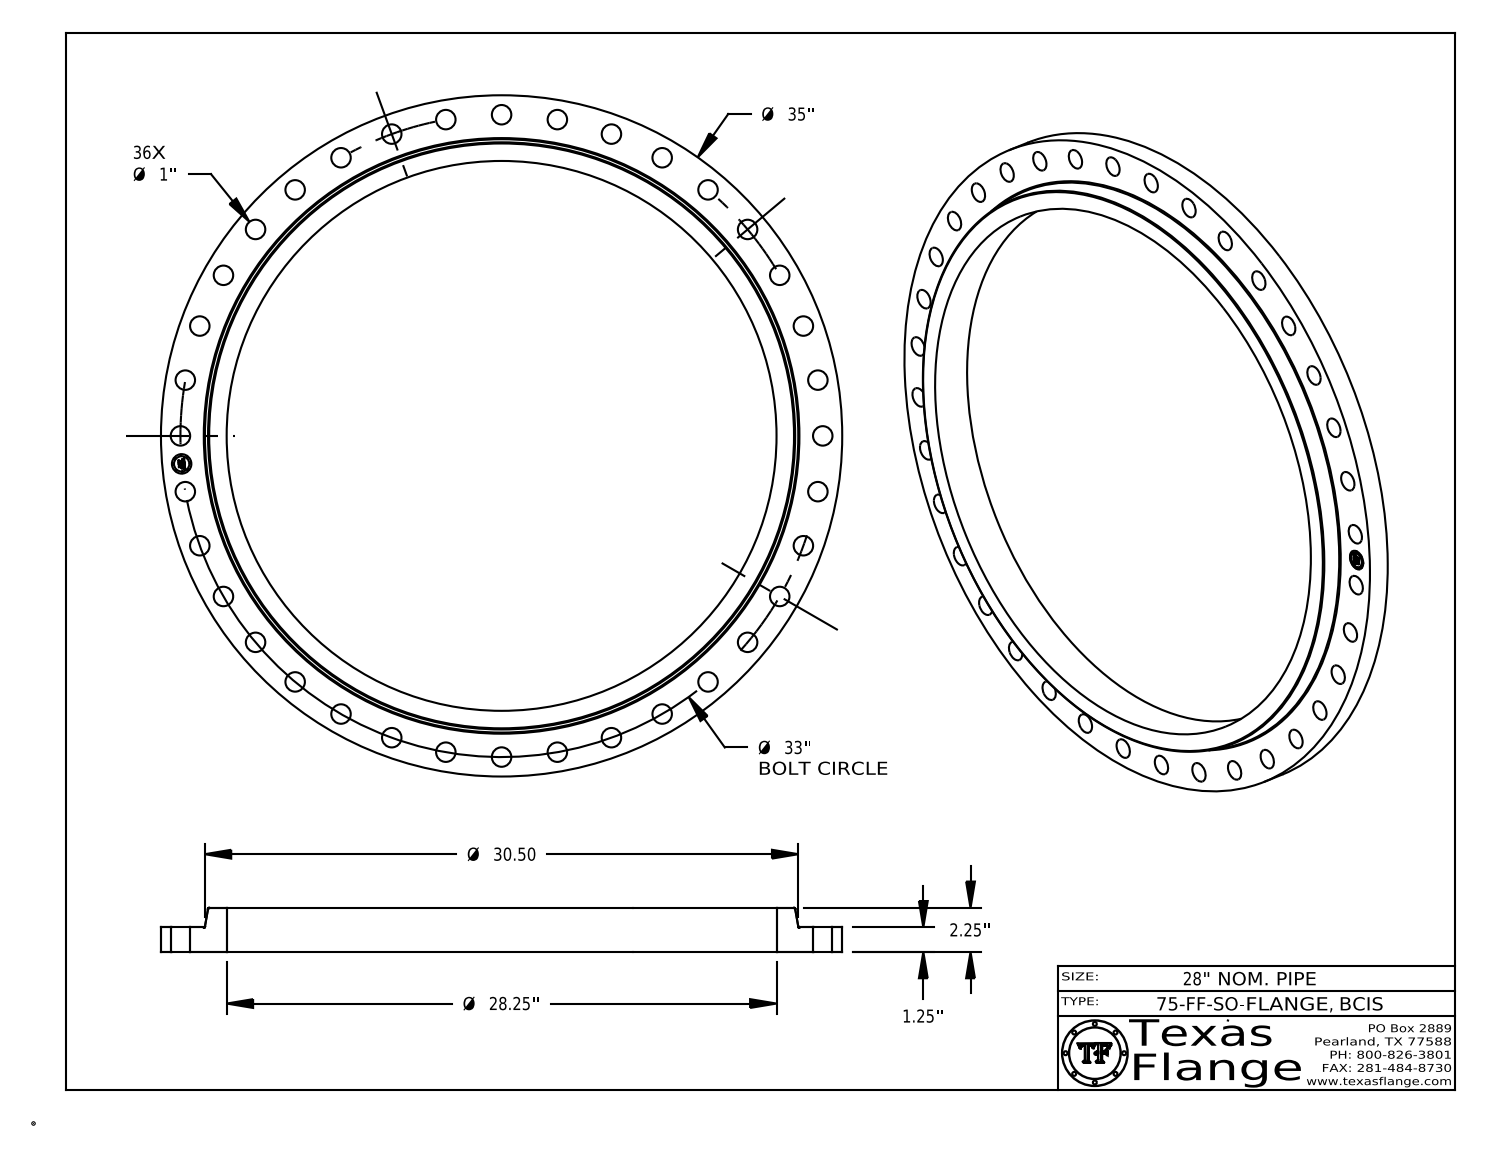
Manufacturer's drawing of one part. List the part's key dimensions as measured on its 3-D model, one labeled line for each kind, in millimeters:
Part name (STEP PRODUCT): BCIS, Class 75-FF-SO
STEP written by: CATIA V5 STEP AP214 (AUTOMOTIVE_DESIGN)
Units: millimetres
Bodies: 1 solid, 470 faces (368 planar, 96 cylindrical, 6 other)
Overall size (bounding box): 889 × 889 × 57.2
Volume: 7 853 000 mm³ · Surface area: 754 200 mm²
Round holes (diameter × count): ⌀25.4 ×37, ⌀717.6 ×1
Round bosses / shafts (diameter × count): ⌀1.5 ×8, ⌀889 ×1, ⌀20 ×1
Main face-to-face distances: 31.8, 57.2, 25.4, 0.4, 31.4, 25.8, 7.6, 7.4, 1.4, 4.9
Hole centre spacings: 419.1, 835, 809.7, 145.5, 286.7, 642.1, 592.7, 787.7
